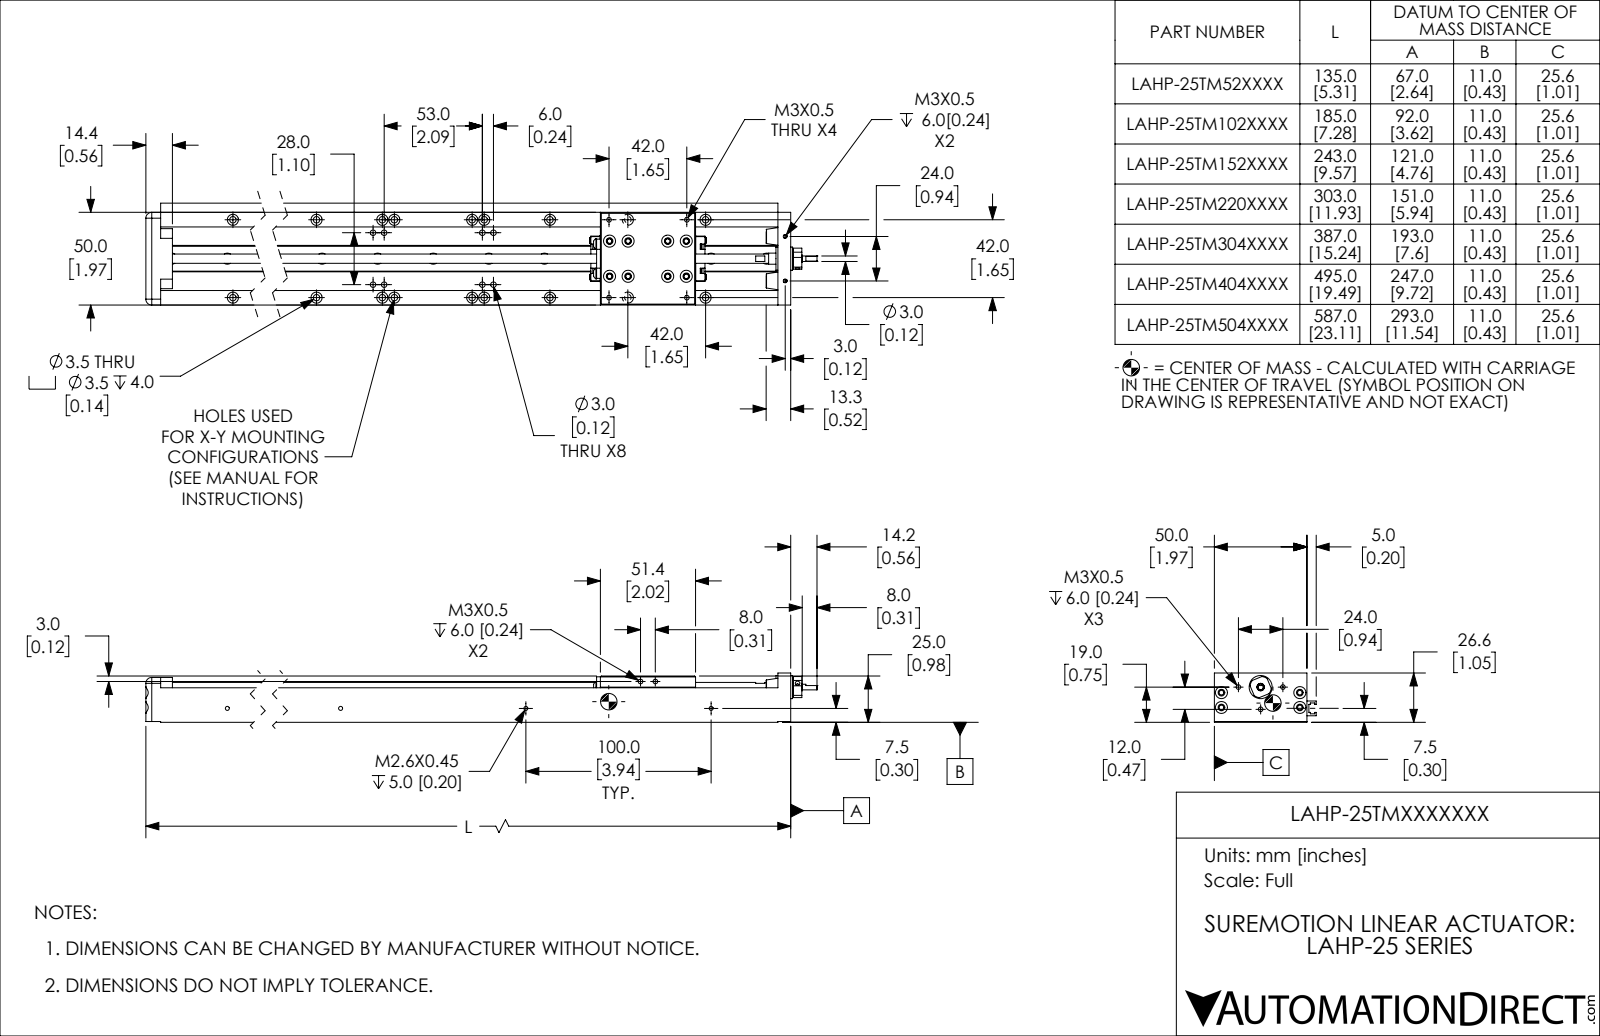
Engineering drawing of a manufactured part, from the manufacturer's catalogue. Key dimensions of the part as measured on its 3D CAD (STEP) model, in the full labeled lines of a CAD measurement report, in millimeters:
Part name (STEP PRODUCT): LAHP-25TM52LP25_BASE; LAHP-25TM52LP25_CARRIAGE; LAHP-25TM52LP25
STEP written by: SolidWorks 2019 (CONFIG_CONTROL_DESIGN)
Units: millimetres
Bodies: 2 solids, 1309 faces (702 planar, 396 cylindrical, 211 other)
Overall size (bounding box): 149.1 × 55 × 26.6
Volume: 112 200 mm³ · Surface area: 52 230 mm²
Round holes (diameter × count): ⌀2.5 ×20, ⌀3.6 ×14, ⌀3 ×12, ⌀3.5 ×12, ⌀6 ×12, ⌀6.5 ×12, ⌀2.5 ×8, ⌀3.3 ×4, ⌀2.1 ×2, ⌀2.2 ×2, ⌀3.1 ×2, ⌀3.4 ×2
Round bosses / shafts (diameter × count): ⌀3 ×5, ⌀5.5 ×4, ⌀5.7 ×2, ⌀2.6 ×2, ⌀12.5 ×1, ⌀8 ×1, ⌀6 ×1, ⌀5 ×1
Partial cylindrical surfaces — rounded edges, fillets, slot ends (radius × count): R3.2 ×5, R3.3 ×4, R0.8 ×2, R0.9 ×2, R1.4 ×2, R1.5 ×2, R1.8 ×2, R5.2 ×2
Main face-to-face distances: 7.9, 42.1, 6, 18.6, 25, 6.4, 5.2, 0.4, 3.5, 1
Hole centre spacings: 47.4, 59, 42, 8, 6, 6.5, 7.1, 7.3
